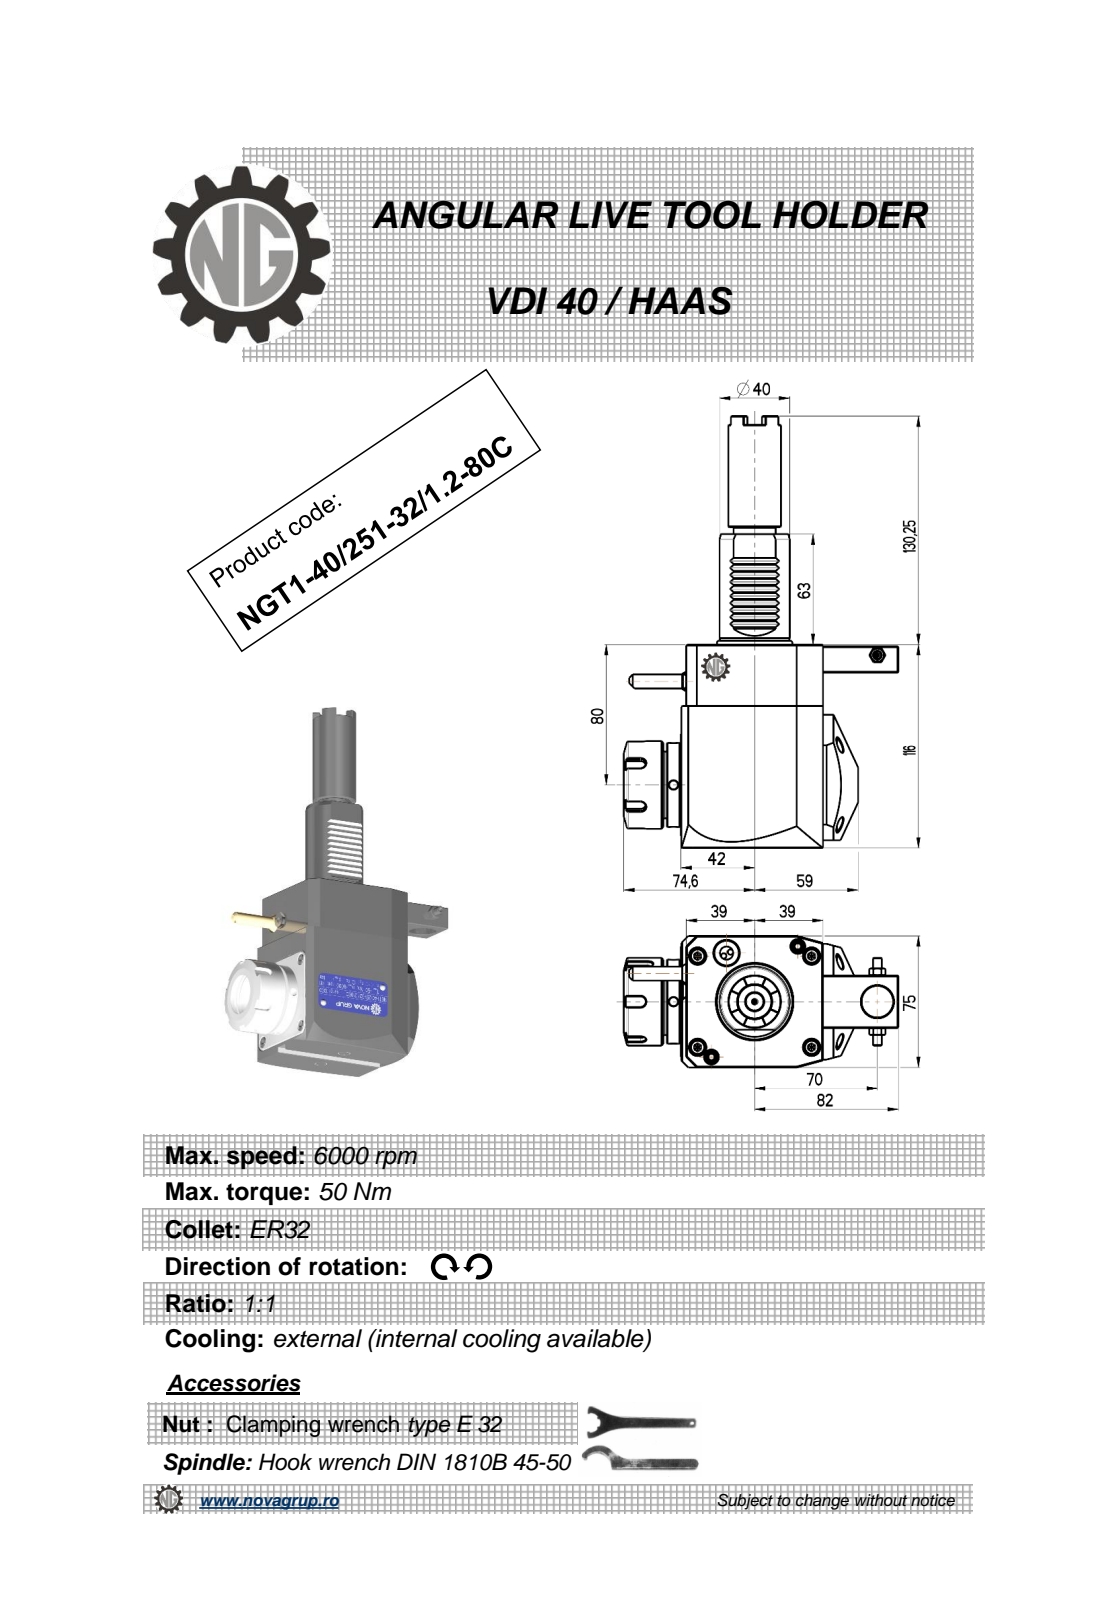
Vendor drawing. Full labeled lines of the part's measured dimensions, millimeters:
Part name (STEP PRODUCT): NGT1_40_251_32_1_2_80C
STEP written by: PRO/ENGINEER BY PARAMETRIC TECHNOLOGY CORPORATION, 2010280 (CONFIG_CONTROL_DESIGN)
Units: millimetres
Bodies: 1 solid, 461 faces (226 planar, 92 cylindrical, 143 other)
Overall size (bounding box): 246.25 × 156.6 × 76.6
Volume: 924 189 mm³ · Surface area: 79 056 mm²
Round holes (diameter × count): ⌀5 ×3, ⌀3 ×1, ⌀4.2 ×1, ⌀9.5 ×1, ⌀18 ×1, ⌀19.5 ×1, ⌀27 ×1
Round bosses / shafts (diameter × count): ⌀50 ×1, ⌀48 ×1, ⌀41 ×1, ⌀40 ×1, ⌀30 ×1, ⌀24 ×1, ⌀10 ×1, ⌀8.96 ×1
Partial cylindrical surfaces — rounded edges, fillets, slot ends (radius × count): R0.26 ×12, R0.3 ×10, R0.2 ×6, R3 ×5, R0.5 ×1, R40 ×1
Main face-to-face distances: 75, 116, 81, 3, 78, 2.8, 80.8, 1, 22.5, 52.5
Hole centre spacings: 20.93, 46.25, 61.13, 70, 72.5, 116.25, 137.8
